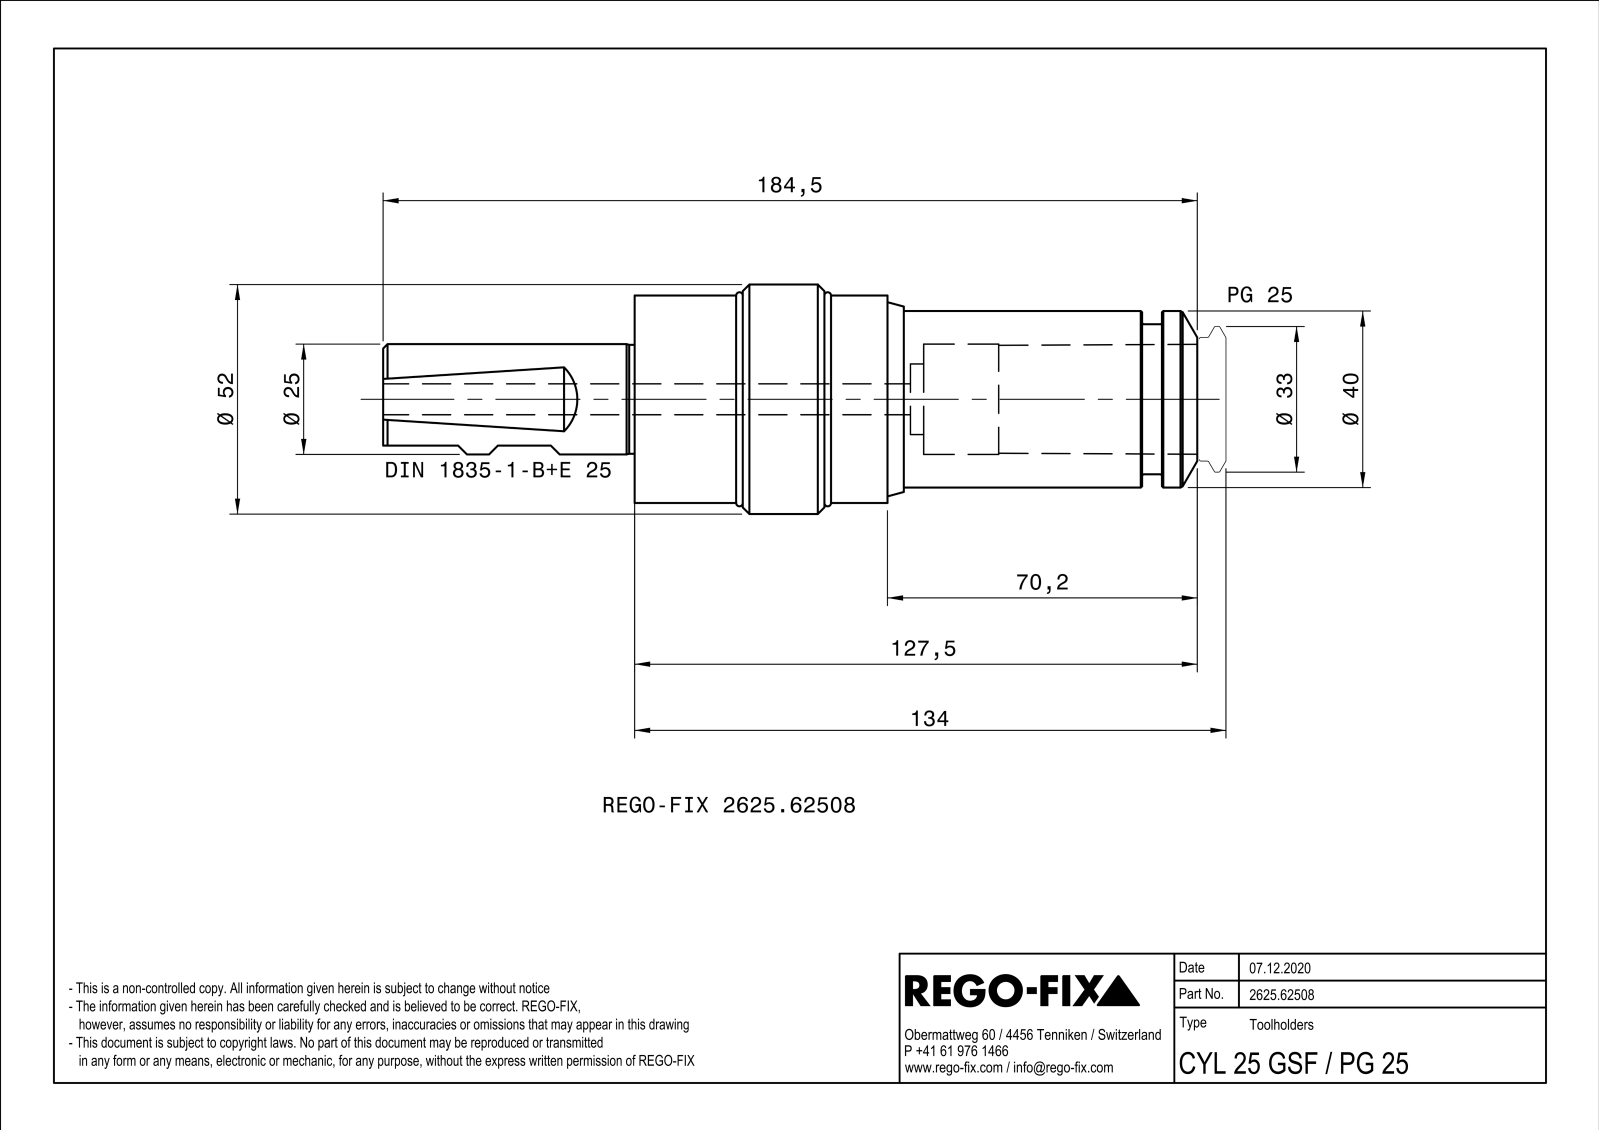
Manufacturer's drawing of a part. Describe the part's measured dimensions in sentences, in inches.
The part is named "MCS_KoSys; F3243G26.1; PCS_KoSys; CSW_KoSys". Its 3-D file was written by "SIEMENS PLM Software Solid Edge ST10 (AUTOMOTIVE_DESIGN)". It is 10 solids with 133 faces: 21 planar, 45 cylindrical and 67 other. Overall it measures 7.266 by 2.047 by 2.047 inches. Its volume is 11.33 cubic inches and its surface area 51.88 square inches. Round holes: 1 of diameter 0.236, 1 of diameter 0.63, 1 of diameter 1.732. Round bosses or shafts: 1 of diameter 2.047, 1 of diameter 1.85, 1 of diameter 1.575, 1 of diameter 1.339, 1 of diameter 0.984, 1 of diameter 0.984. Partial cylindrical surfaces (rounded edges, fillets, slot ends): 1 of radius 0.063. The main face-to-face distances are 2.244, 4.705, 0.177, 2.126, 2.579, 4.823, 1.949, 4.528, 6.772, 6.949.
